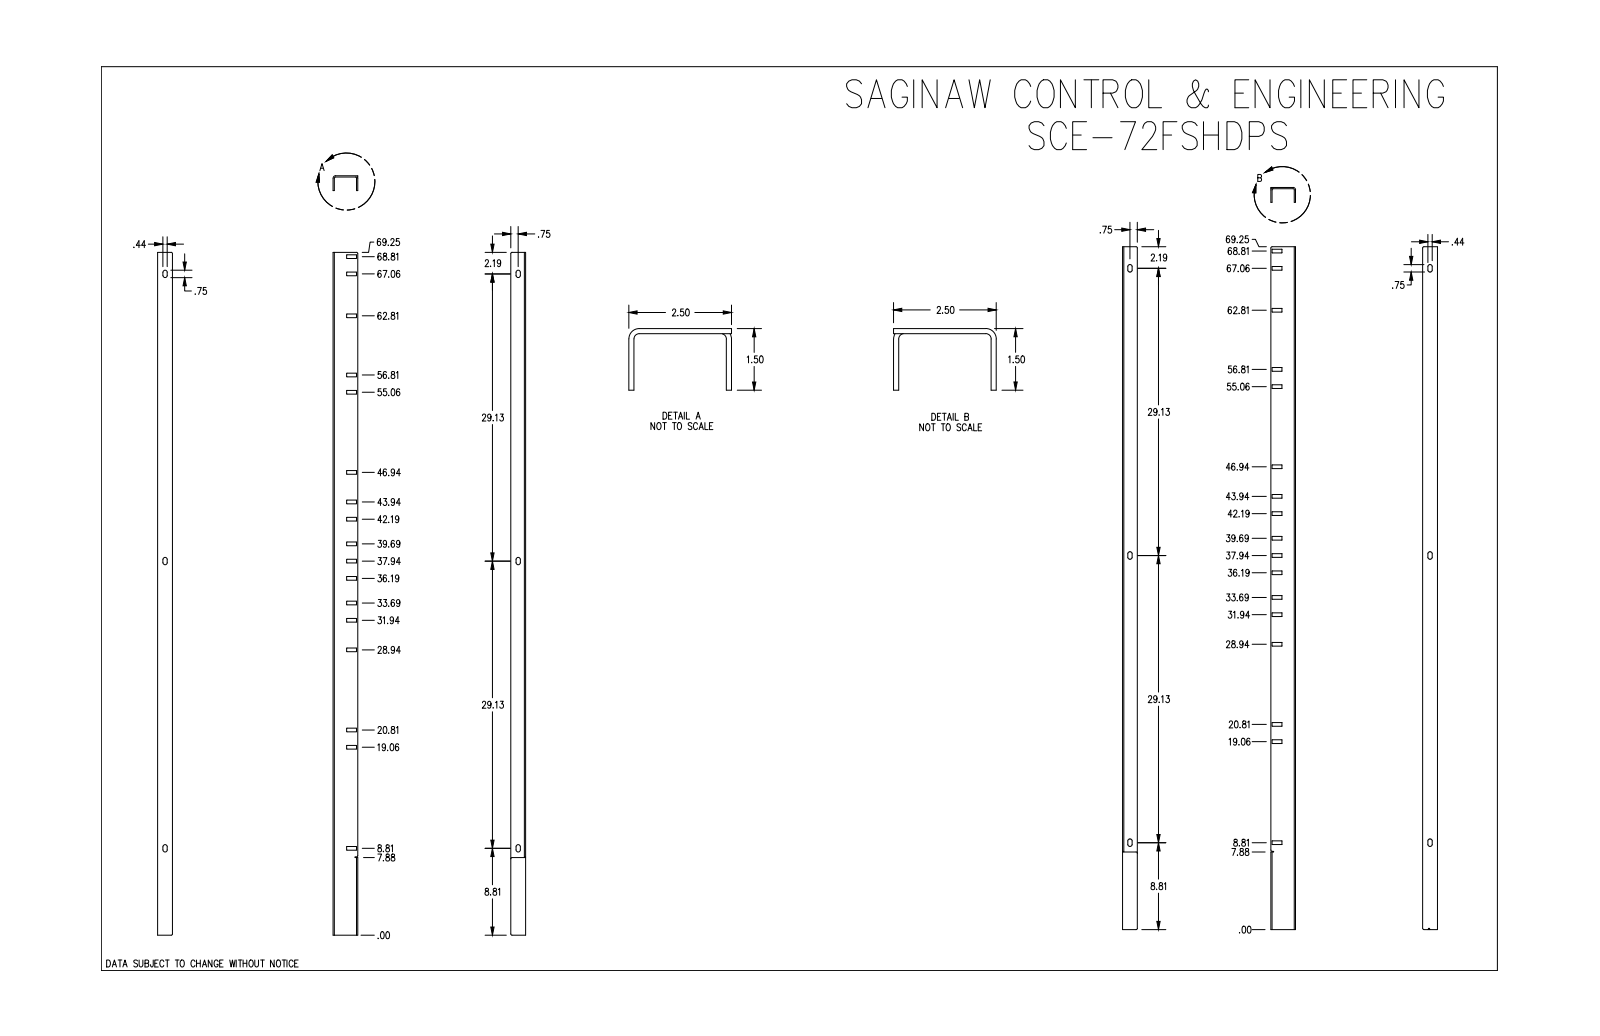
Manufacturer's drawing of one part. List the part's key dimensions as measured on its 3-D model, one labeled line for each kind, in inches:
Part name (STEP PRODUCT): SCE-72FSHDPS
STEP written by: SolidWorks 2019 (CONFIG_CONTROL_DESIGN)
Units: inches
Bodies: 2 solids, 364 faces (184 planar, 180 cylindrical, 0 other)
Overall size (bounding box): 69.25 × 12 × 1.5
Volume: 66.4 in³ · Surface area: 1 113 in²
Partial cylindrical surfaces — rounded edges, fillets, slot ends (radius × count): R0.03 ×70, R0.02 ×67, R0.188 ×12, R0.13 ×10, R0.219 ×6, R0.031 ×3, R0.255 ×3, R0.015 ×2
Main face-to-face distances: 0.125, 0.125, 11.875, 12, 11.75, 2.5, 9.5, 9.375, 2.375, 2.375
